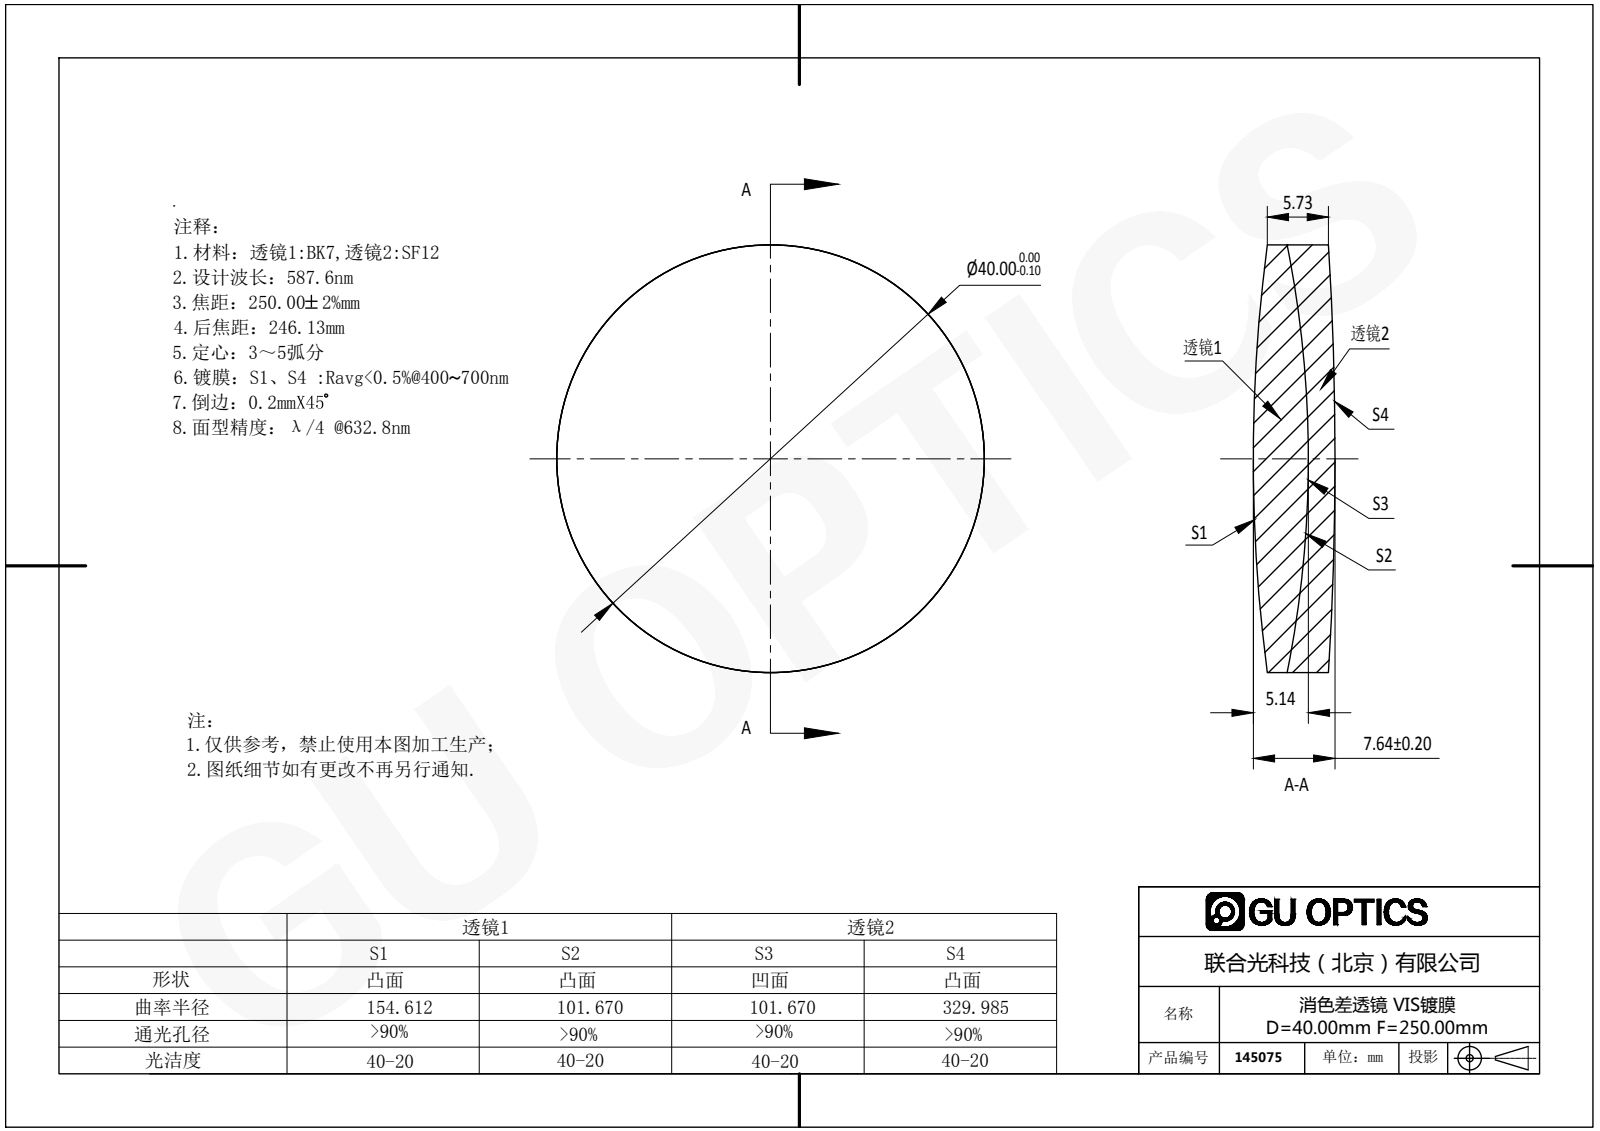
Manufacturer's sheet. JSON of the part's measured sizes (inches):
{"part_name": "145075", "step_written_by": "SolidWorks 2016 (AUTOMOTIVE_DESIGN)", "units": "inches", "bodies": {"solids": 2, "faces": 12, "planar": 0, "cylindrical": 4, "other": 8}, "overall_size": [1.575, 1.575, 0.301], "volume_in3": 0.513, "surface_area_in2": 8.956, "round_bosses_or_shafts": [[1.575, 1]]}
